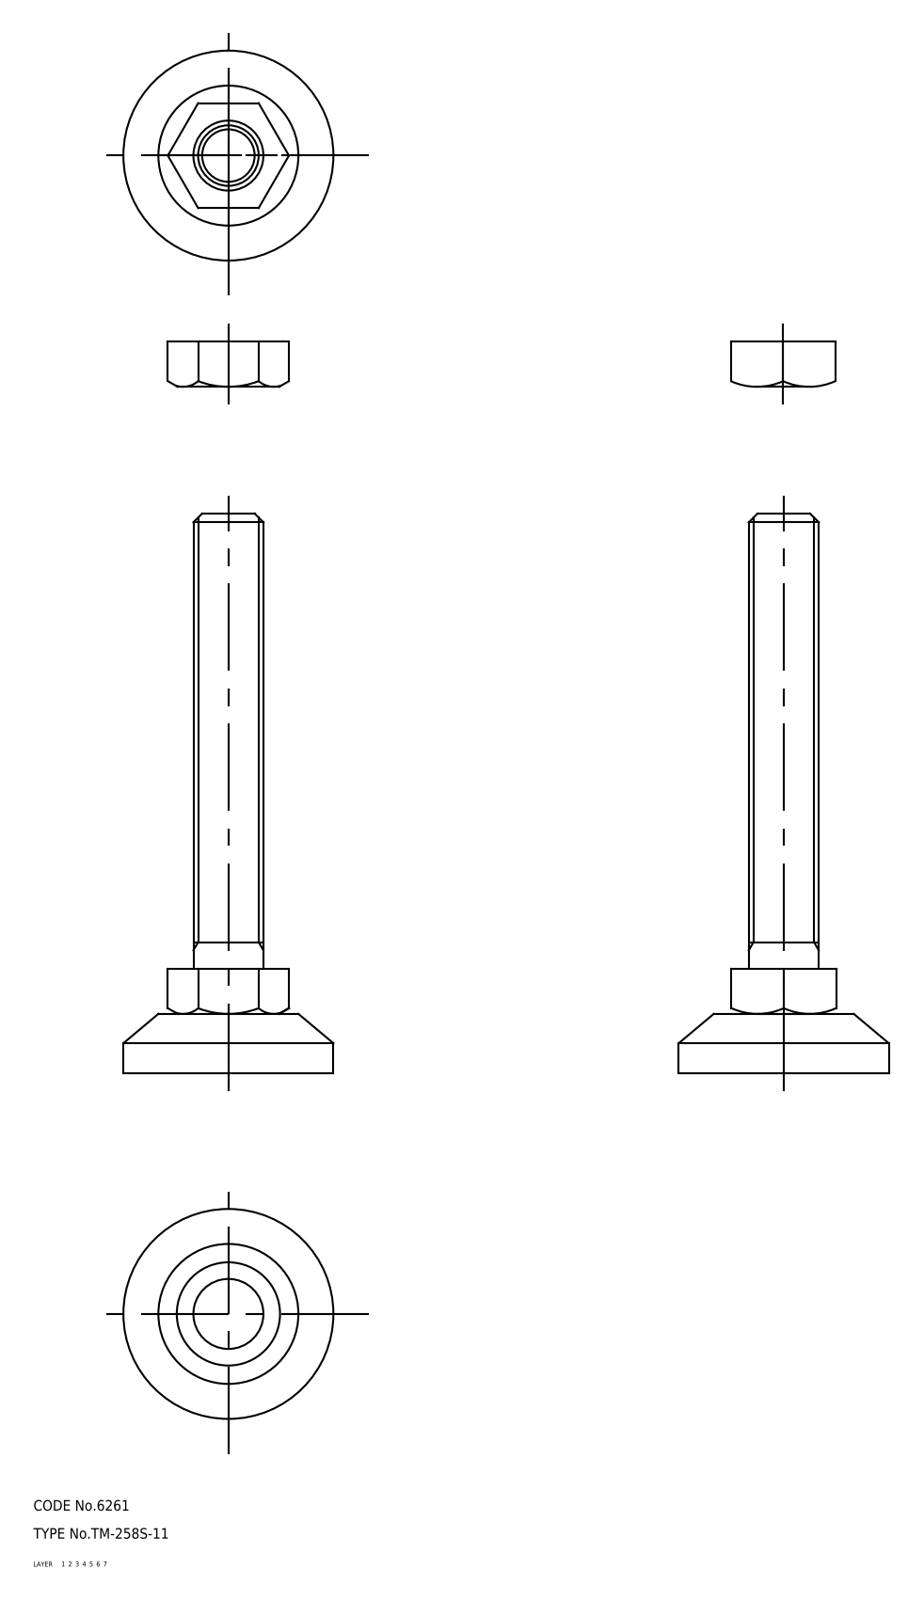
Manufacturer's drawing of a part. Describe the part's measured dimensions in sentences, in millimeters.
The part is named "67112318; 67112331; 67112344". Its 3-D file was written by "CADfix (AUTOMOTIVE_DESIGN)". It is 3 solids with 67 faces: 0 planar, 0 cylindrical and 67 other. Overall it measures 160 by 60 by 60 millimeters. Its volume is 89 441 cubic millimeters and its surface area 23 464 square millimeters.
